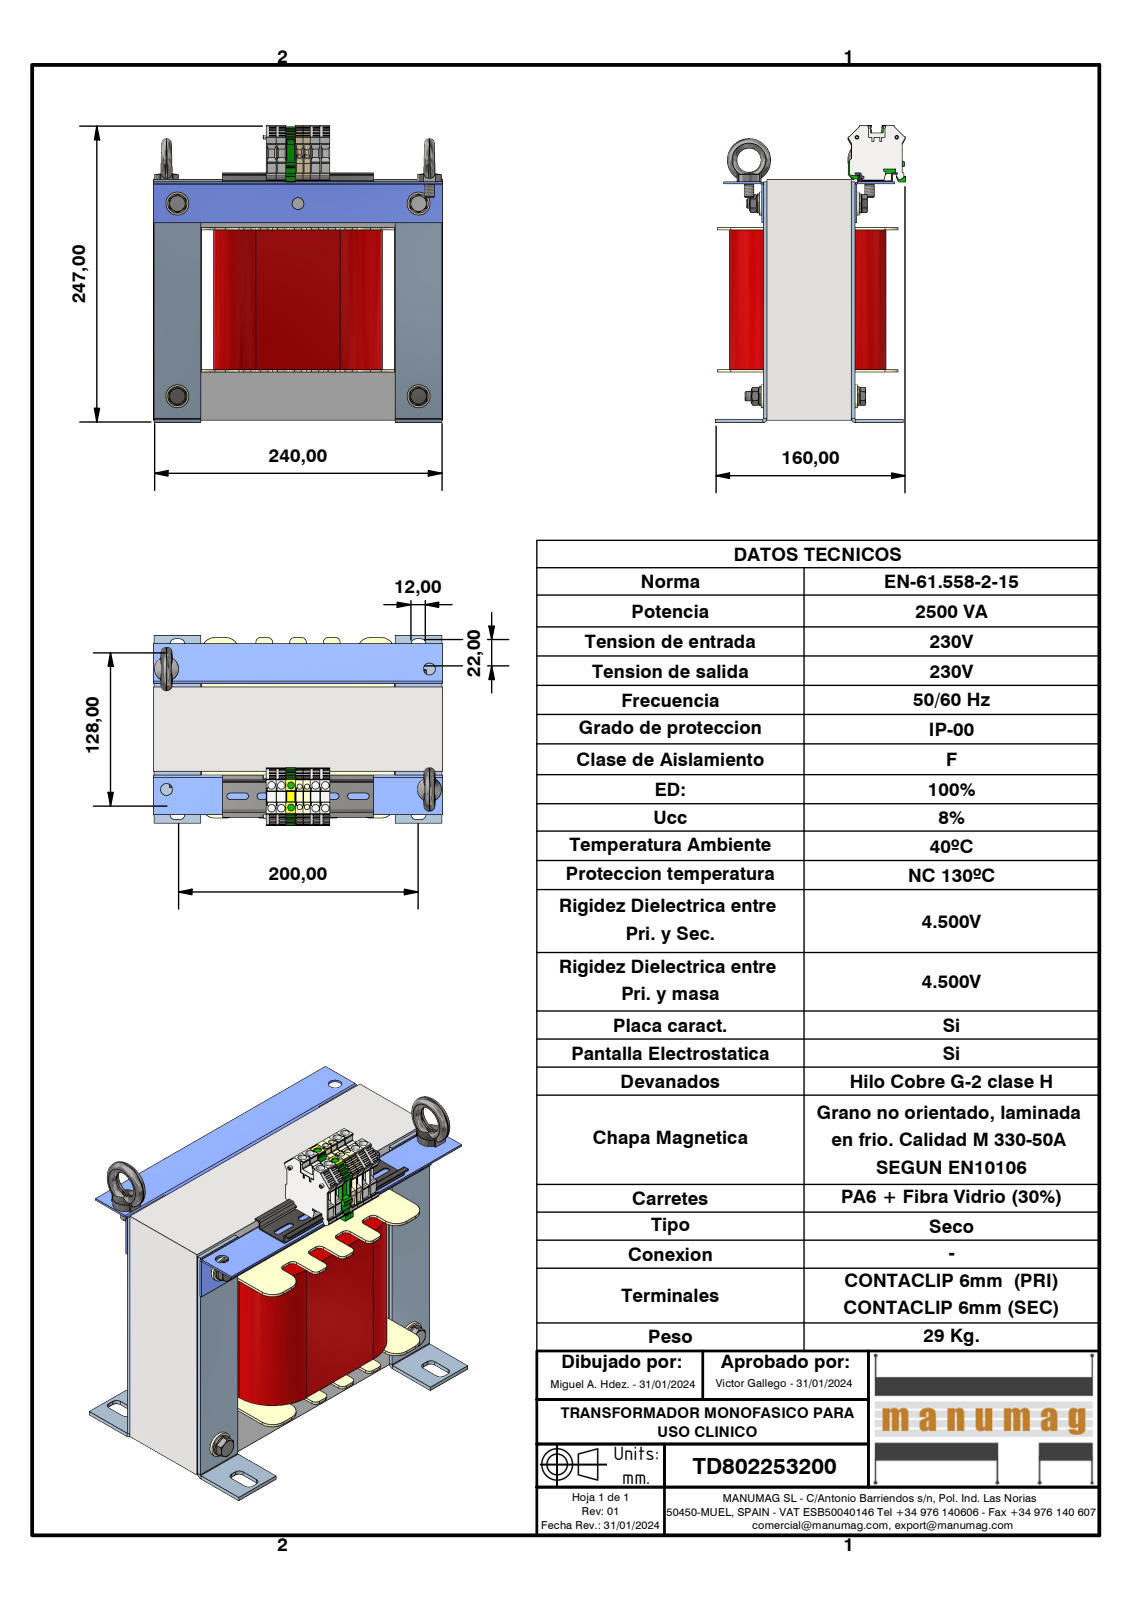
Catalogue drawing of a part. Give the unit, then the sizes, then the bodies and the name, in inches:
Units: inches
Overall size (bounding box): 9.726 × 9.449 × 6.224
Round holes (diameter × count): ⌀0.248 ×8, ⌀0.394 ×7, ⌀0.094 ×4, ⌀0.098 ×4, ⌀0.108 ×4, ⌀0.169 ×4, ⌀0.262 ×4, ⌀0.315 ×4, ⌀0.331 ×4, ⌀0.433 ×4, ⌀0.472 ×4, ⌀0.116 ×2
Round bosses / shafts (diameter × count): ⌀0.748 ×4, ⌀0.63 ×4, ⌀0.449 ×4, ⌀0.378 ×4, ⌀0.288 ×4, ⌀1.417 ×2, ⌀0.315 ×2, ⌀0.276 ×2
Partial cylindrical surfaces — rounded edges, fillets, slot ends (radius × count): R0.157 ×48, R0.012 ×30, R0.039 ×22, R0.01 ×17, R0.02 ×13, R0.102 ×10, R0.079 ×9, R0.016 ×8
Main face-to-face distances: 1.575, 6.299, 2.756, 0.118, 3.15, 2.874, 7.874, 0.079, 4.724, 0.059
Hole centre spacings: 3.937, 0.319, 0.6, 0.748, 0.813, 0.839, 0.928, 1.098
Volume: 265.1 in³ · Surface area: 866.6 in²
Bodies: 42 solids, 2415 faces (1680 planar, 567 cylindrical, 168 other)
Part name (STEP PRODUCT): TD802253200; EI240 240 x 200 - 70 (Rc80); SEMI 40 X 60 RC80 EI240 - 35; Escuadra RC80 (+8 more)
STEP written by: Autodesk Inventor 2023 (AUTOMOTIVE_DESIGN)
